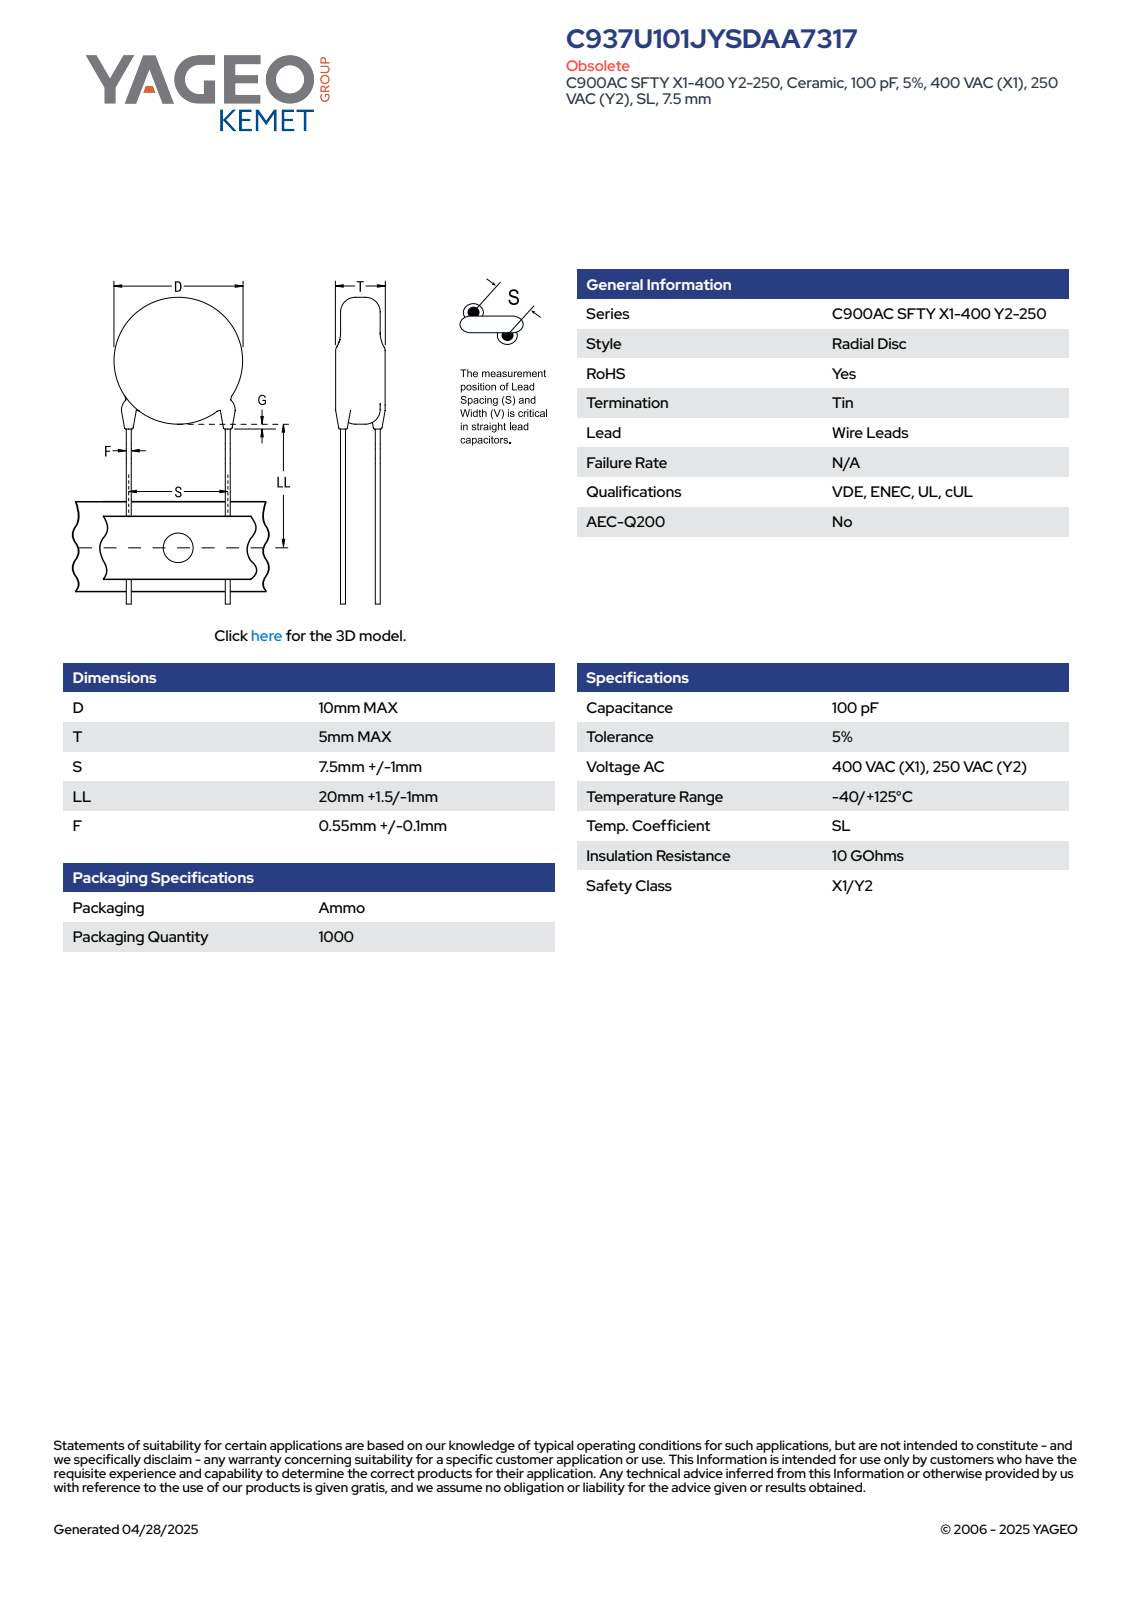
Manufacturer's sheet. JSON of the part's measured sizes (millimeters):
{"part_name": "CCD_STC900_D10T5S7.5LL21.5F0.65G3", "step_written_by": "SolidWorks 2014 (AUTOMOTIVE_DESIGN)", "units": "millimeters", "bodies": {"solids": 4, "faces": 83, "planar": 61, "cylindrical": 6, "other": 16}, "overall_size": [31.5, 10, 5], "volume_mm3": 396, "surface_area_mm2": 388, "round_bosses_or_shafts": [[0.65, 2], [10, 1]], "face_to_face_distances": [5, 27.07, 25.92, 1.15, 0.93, 0.42, 0.31, 3.43, 3.56, 1.89]}
